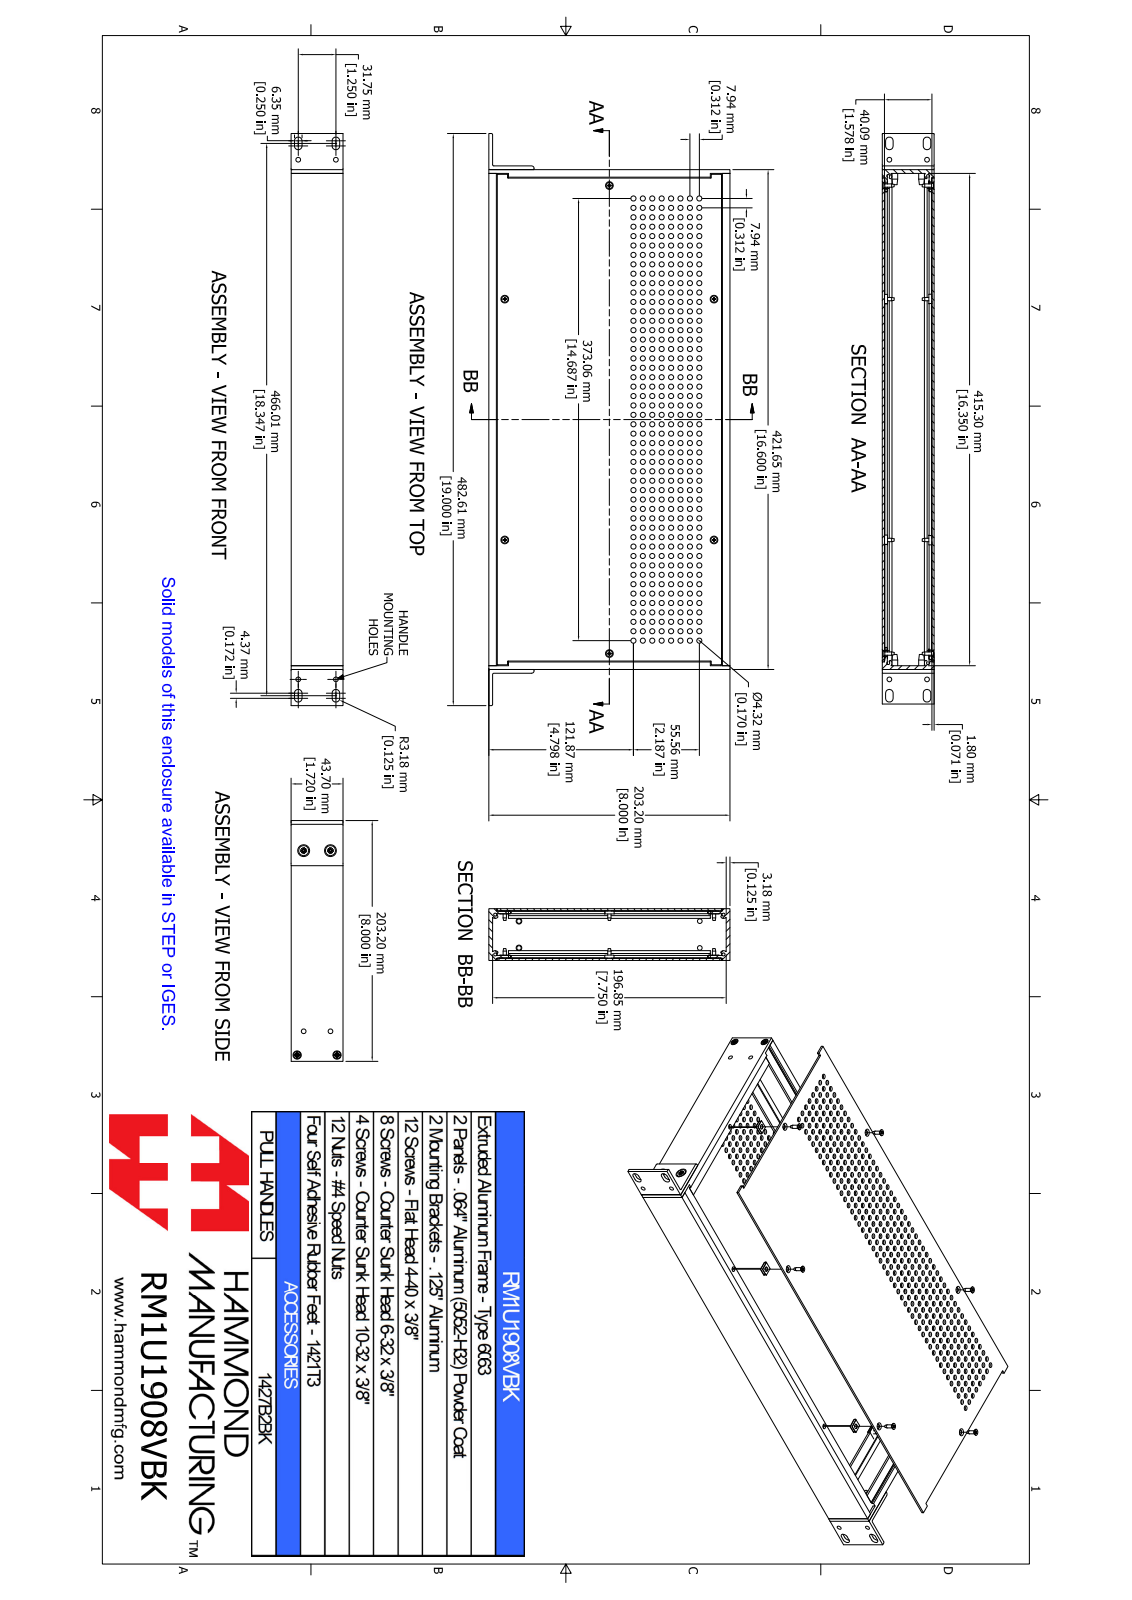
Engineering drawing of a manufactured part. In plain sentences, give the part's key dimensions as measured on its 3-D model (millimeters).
The part is named "RM1U1908VBK". Its 3-D file was written by "SolidWorks 2021 (AUTOMOTIVE_DESIGN)". It is 44 solids with 1952 faces: 564 planar, 956 cylindrical and 432 other. Overall it measures 482.6 by 203.2 by 43.7 millimeters. Its volume is 550 800 cubic millimeters and its surface area 527 200 square millimeters. Round holes: 384 of diameter 4.3, 6 of diameter 2.5, 6 of diameter 4, 6 of diameter 4.3, 4 of diameter 3.5, 4 of diameter 4, 4 of diameter 4, 2 of diameter 5. Round bosses or shafts: 6 of diameter 5.4, 6 of diameter 2.8, 4 of diameter 6, 4 of diameter 3.5, 2 of diameter 8.5, 2 of diameter 4.8. Partial cylindrical surfaces (rounded edges, fillets, slot ends): 18 of radius 1, 16 of radius 3.2, 12 of radius 1.2, 8 of radius 1.3, 6 of radius 1, 4 of radius 0.9, 2 of radius 2. The main face-to-face distances are 1.8, 41.9, 43.7, 40.1, 37.6, 3.2, 4.2, 39.4, 2.4, 3.2. The hole center spacings are 17.8, 8, 15.9, 25.1, 32.7, 7.9, 11.2, 31.8.
